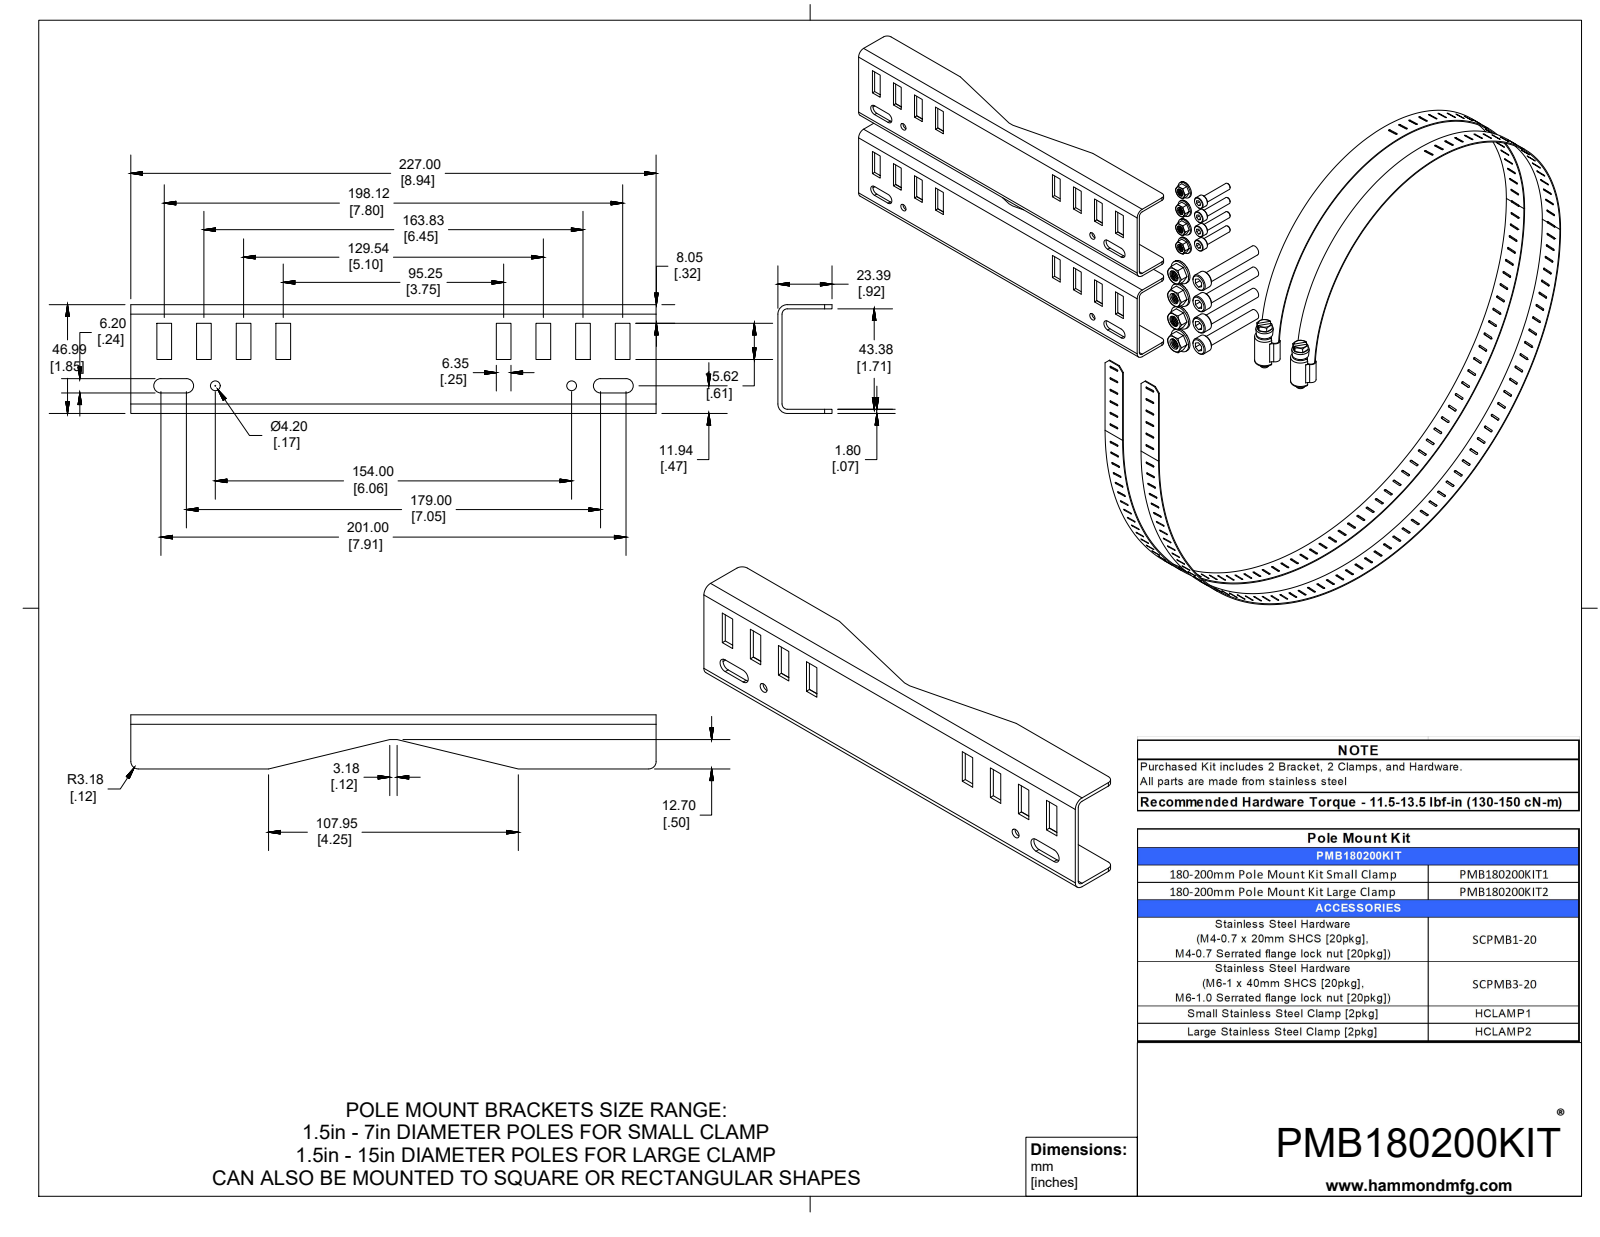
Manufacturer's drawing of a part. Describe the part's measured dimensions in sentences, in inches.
The part is named "PMB180200KIT1". Its 3-D file was written by "SolidWorks 2019 (CONFIG_CONTROL_DESIGN)". It is 22 solids with 1818 faces: 1220 planar, 476 cylindrical and 122 other. Overall it measures 14.558 by 12.897 by 10.397 inches. Its volume is 5.487 cubic inches and its surface area 217.5 square inches. Round holes: 4 of diameter 0.13, 4 of diameter 0.166, 4 of diameter 0.185, 4 of diameter 0.197, 4 of diameter 0.236. Round bosses or shafts: 8 of diameter 0.394, 4 of diameter 0.559, 4 of diameter 0.416, 4 of diameter 0.293, 4 of diameter 0.272, 4 of diameter 0.236, 4 of diameter 0.157, 2 of diameter 0.313. Partial cylindrical surfaces (rounded edges, fillets, slot ends): 364 of radius 0.02, 9 of radius 0.125, 8 of radius 0.122, 4 of radius 0.09, 4 of radius 0.1, 4 of radius 0.12, 4 of radius 0.161, 2 of radius 0.195. The main face-to-face distances are 0.071, 2.244, 1.779, 2.315, 1.708, 4.022, 0.394, 0.465, 0.071, 4.093. The hole center spacings are 0.513, 0.63, 1.027, 1.259, 2.244, 6.063, 6.465, 0.63.
